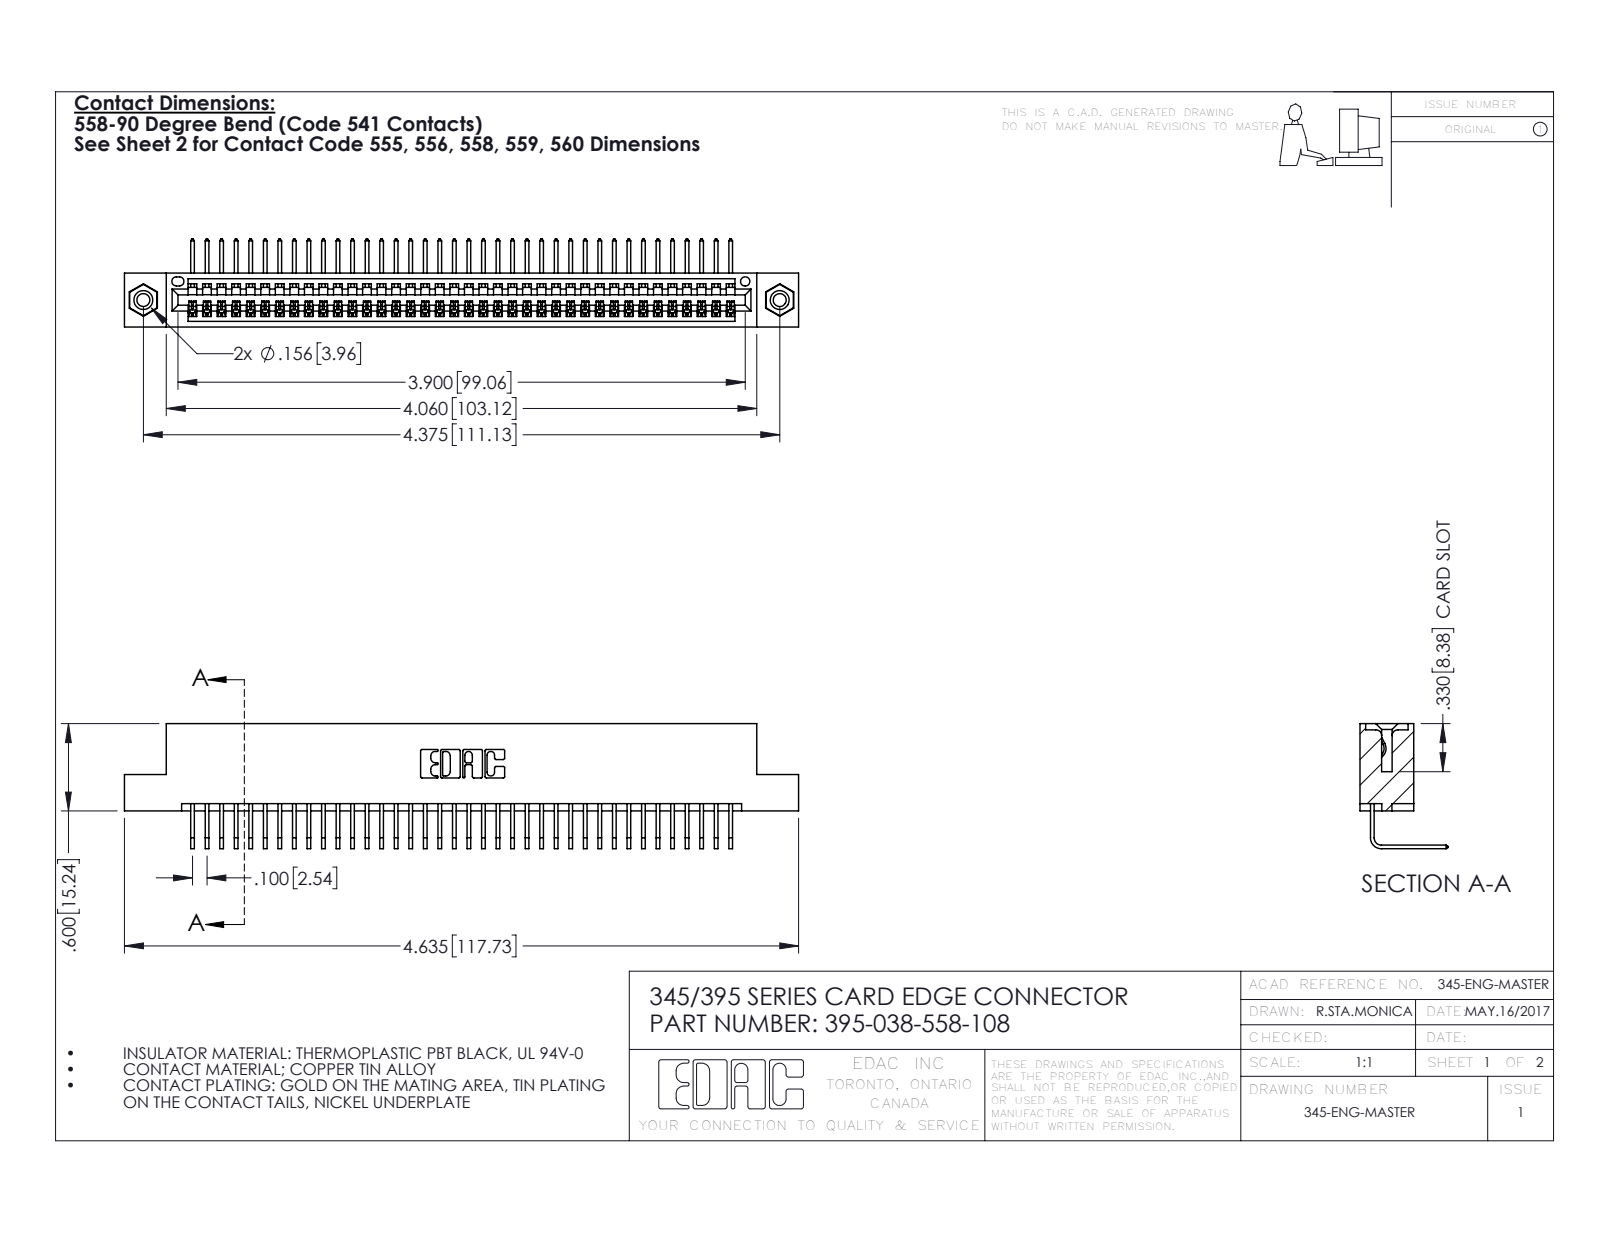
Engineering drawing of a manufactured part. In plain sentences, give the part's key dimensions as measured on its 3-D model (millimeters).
The part is named "345 Part_Flush Mounting Lugs - 0.156 Dia-TI; 345-250-001_345-250-003-102; 395-038-558-108; 345-292-001_558 Tail - 2". Its 3-D file was written by "SolidWorks 2016 (CONFIG_CONTROL_DESIGN)". It is 41 solids with 2466 faces: 1708 planar, 742 cylindrical and 16 other. Overall it measures 117.7 by 21.8 by 15.4 millimeters. Its volume is 11 300 cubic millimeters and its surface area 15 680 square millimeters. Round holes: 2 of diameter 2.3, 2 of diameter 3.2, 2 of diameter 4, 1 of diameter 1.6. Round bosses or shafts: 2 of diameter 3.9. Partial cylindrical surfaces (rounded edges, fillets, slot ends): 76 of radius 0.2, 22 of radius 0.3, 6 of radius 0.2, 6 of radius 0.8, 3 of radius 0.7, 2 of radius 0.8, 2 of radius 1, 1 of radius 0.4. The main face-to-face distances are 1.8, 7.6, 9.4, 5.1, 2.5, 6.9, 0.6, 5.7, 3.8, 1.8. The hole center spacings are 6.9, 105.1, 111.1.
